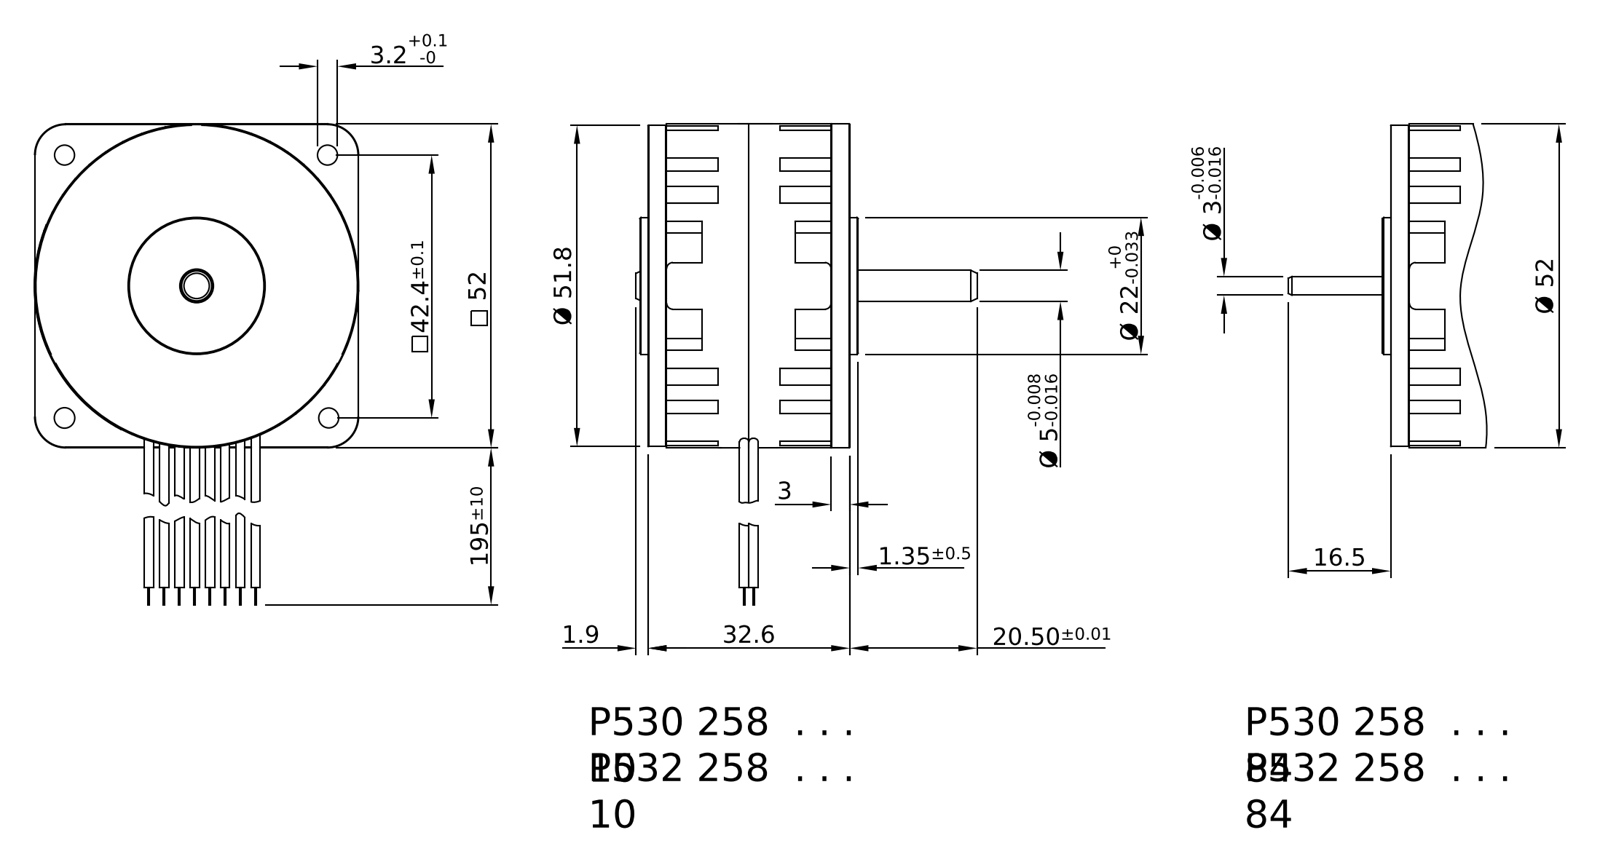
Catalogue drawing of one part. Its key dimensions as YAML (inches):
part_name: "2800500017_D_FAUT_1; 2420500042_D_FAUT_ASM_1_ASM; 2800500015_D_FAUT_1; 280050011203_D_FAUT_1 (+8 more)"
step_written_by: "PRO/ENGINEER BY PARAMETRIC TECHNOLOGY CORPORATION, 2014310 (CONFIG_CONTROL_DESIGN)"
units: inches
bodies: {solids: 25, faces: 2601, planar: 365, cylindrical: 282, other: 1954}
overall_size: [3.205, 2.74, 2.047]
volume: 4.076
surface_area: 51.52
round_holes:
  - {diameter: 0.087, count: 8}
  - {diameter: 0.079, count: 4}
  - {diameter: 0.126, count: 4}
  - {diameter: 0.118, count: 3}
  - {diameter: 0.122, count: 3}
  - {diameter: 0.059, count: 1}
  - {diameter: 0.866, count: 1}
round_bosses_or_shafts:
  - {diameter: 0.05, count: 8}
  - {diameter: 0.031, count: 8}
  - {diameter: 0.177, count: 3}
  - {diameter: 2.047, count: 1}
  - {diameter: 2.039, count: 1}
  - {diameter: 0.197, count: 1}
  - {diameter: 0.118, count: 1}
partial_cylinders:
  - {radius: 0.004, count: 8}
  - {radius: 0.039, count: 4}
  - {radius: 0.197, count: 4}
  - {radius: 0.076, count: 3}
  - {radius: 0.866, count: 1}
  - {radius: 0.951, count: 1}
face_to_face_distances: [0.52, 1.039, 0.118, 1.157, 0.638, 0.091, 0.039, 0.126, 1.283, 1.165]
hole_center_spacings: [0.921, 0.906, 0.095, 0.189, 0.376, 0.839, 1.18, 1.669]
